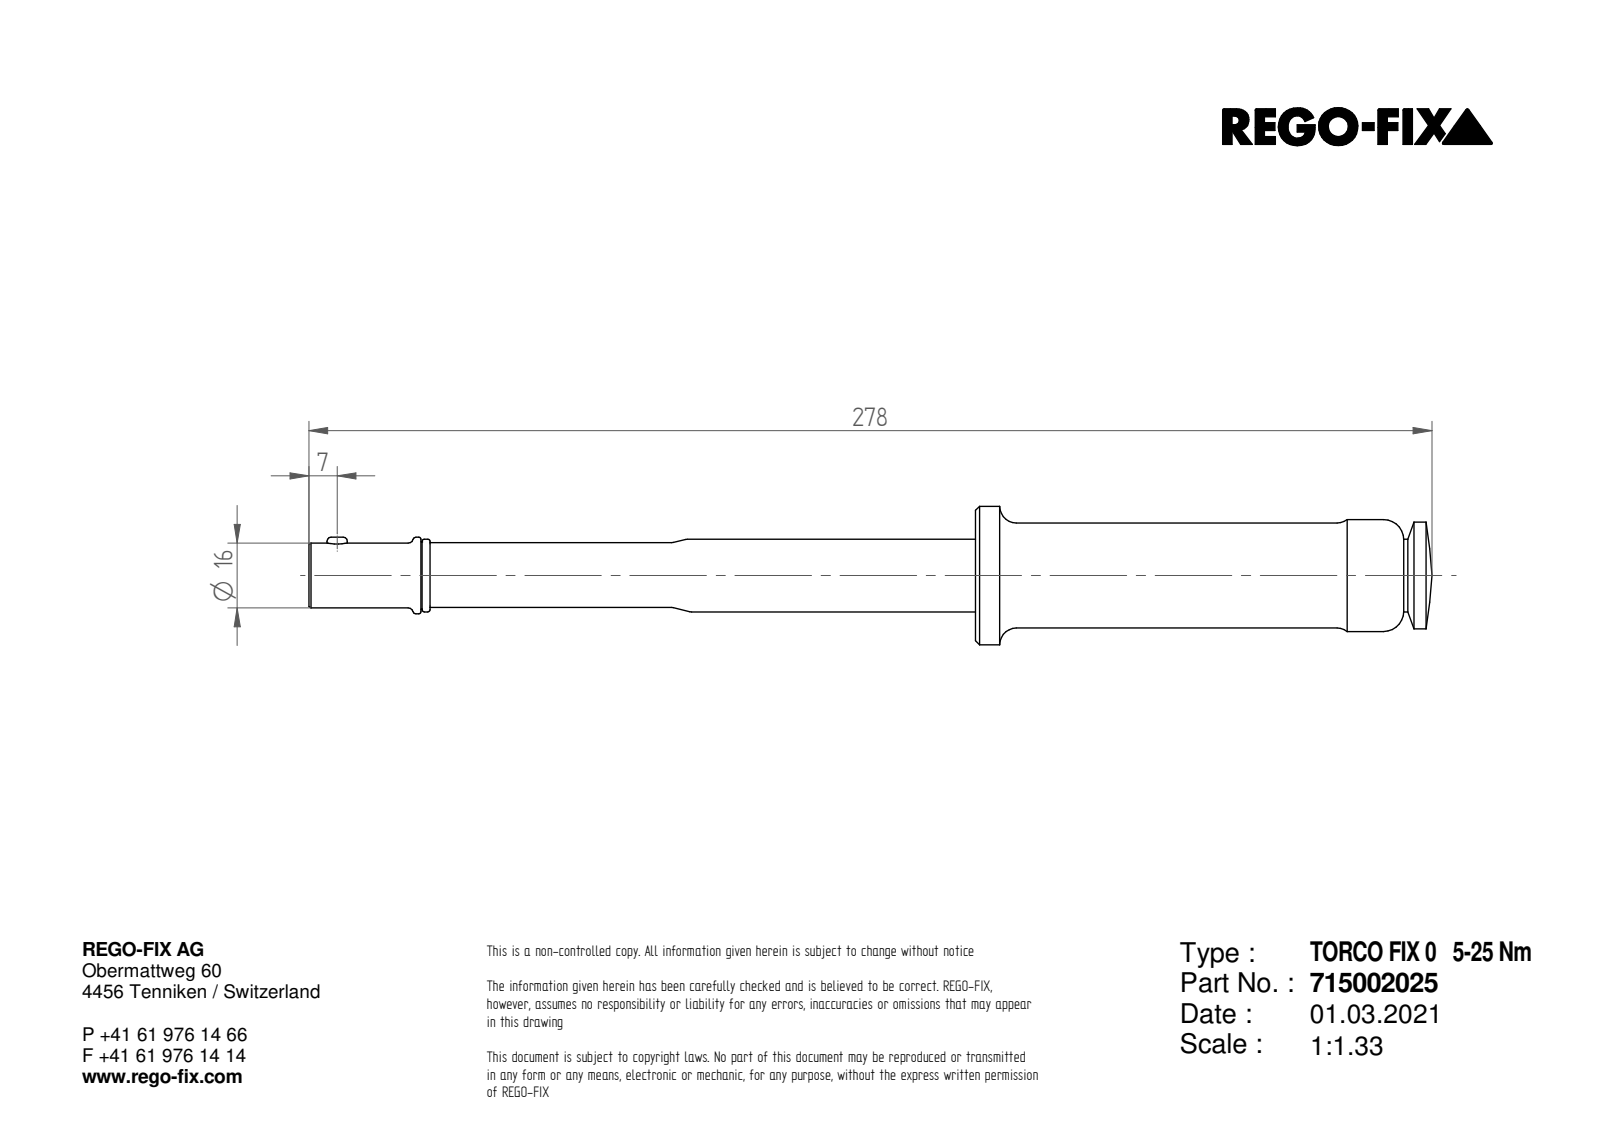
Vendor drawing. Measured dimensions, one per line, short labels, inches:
name: 6219-1 TORCO-FIX 0 Adjustable Torque Wrench 5-25 Nm (16mm interface); 6219-2 TORCO-FIX 0 Adjustable Torque Wrench 5-25 Nm (16mm interface); 6219 TORCO-FIX 0 Adjustable Torque Wrench 5-25 Nm (16mm interface)
written by: Alibre (AUTOMOTIVE_DESIGN)
unit: in
bodies: 2 solids, 60 faces (18 planar, 20 cylindrical, 22 other)
size: 10.945 × 1.348 × 1.348
volume: 7.605 in³; area: 41.35 in²
bosses: 1× ⌀1.348, 1× ⌀1.091, 1× ⌀1.053, 1× ⌀1.039, 1× ⌀1.024, 1× ⌀0.748, 1× ⌀0.709, 1× ⌀0.652
rounds: 6× R0.079, 1× R0.787
face distances: 0.561, 0.63, 0.069, 6.496, 3.543, 2.953, 1.093, 2.451, 5.404, 1.181
